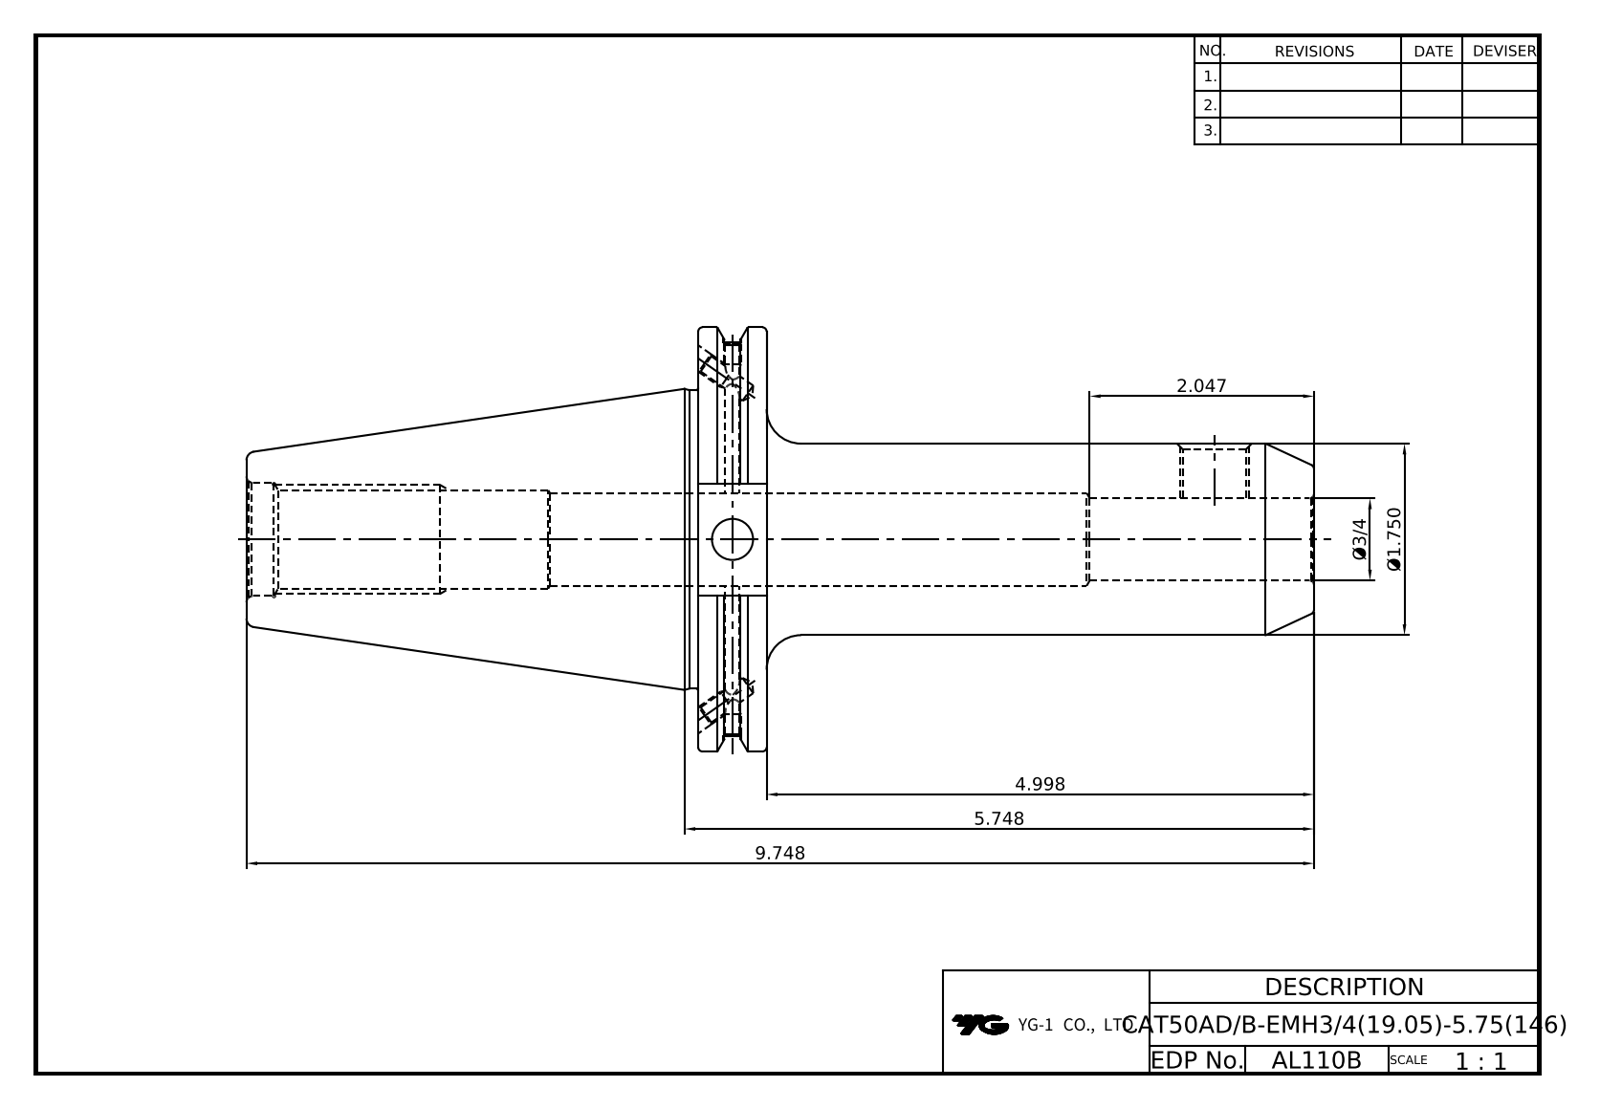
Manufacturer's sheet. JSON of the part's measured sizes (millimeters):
{"part_name": "LO-CAT50ADB-EMH19.05-146", "step_written_by": "Autodesk Inventor 2024 (AUTOMOTIVE_DESIGN)", "units": "millimeters", "bodies": {"solids": 1, "faces": 85, "planar": 36, "cylindrical": 26, "other": 23}, "overall_size": [247.6, 98.42, 94.69], "volume_mm3": 468855, "surface_area_mm2": 70196, "round_holes": [[3.24, 2], [4.13, 2], [4.2, 2], [5, 2], [9.53, 1], [14.35, 1], [19.05, 1], [21.5, 1], [21.97, 1], [26.2, 1]], "round_bosses_or_shafts": [[98.42, 1], [91.29, 1], [69.25, 1], [44.45, 1]], "face_to_face_distances": [15.88, 142.83, 126.95, 104.77, 120.65, 247.6, 73.03, 25.9, 110.82, 6.05]}
